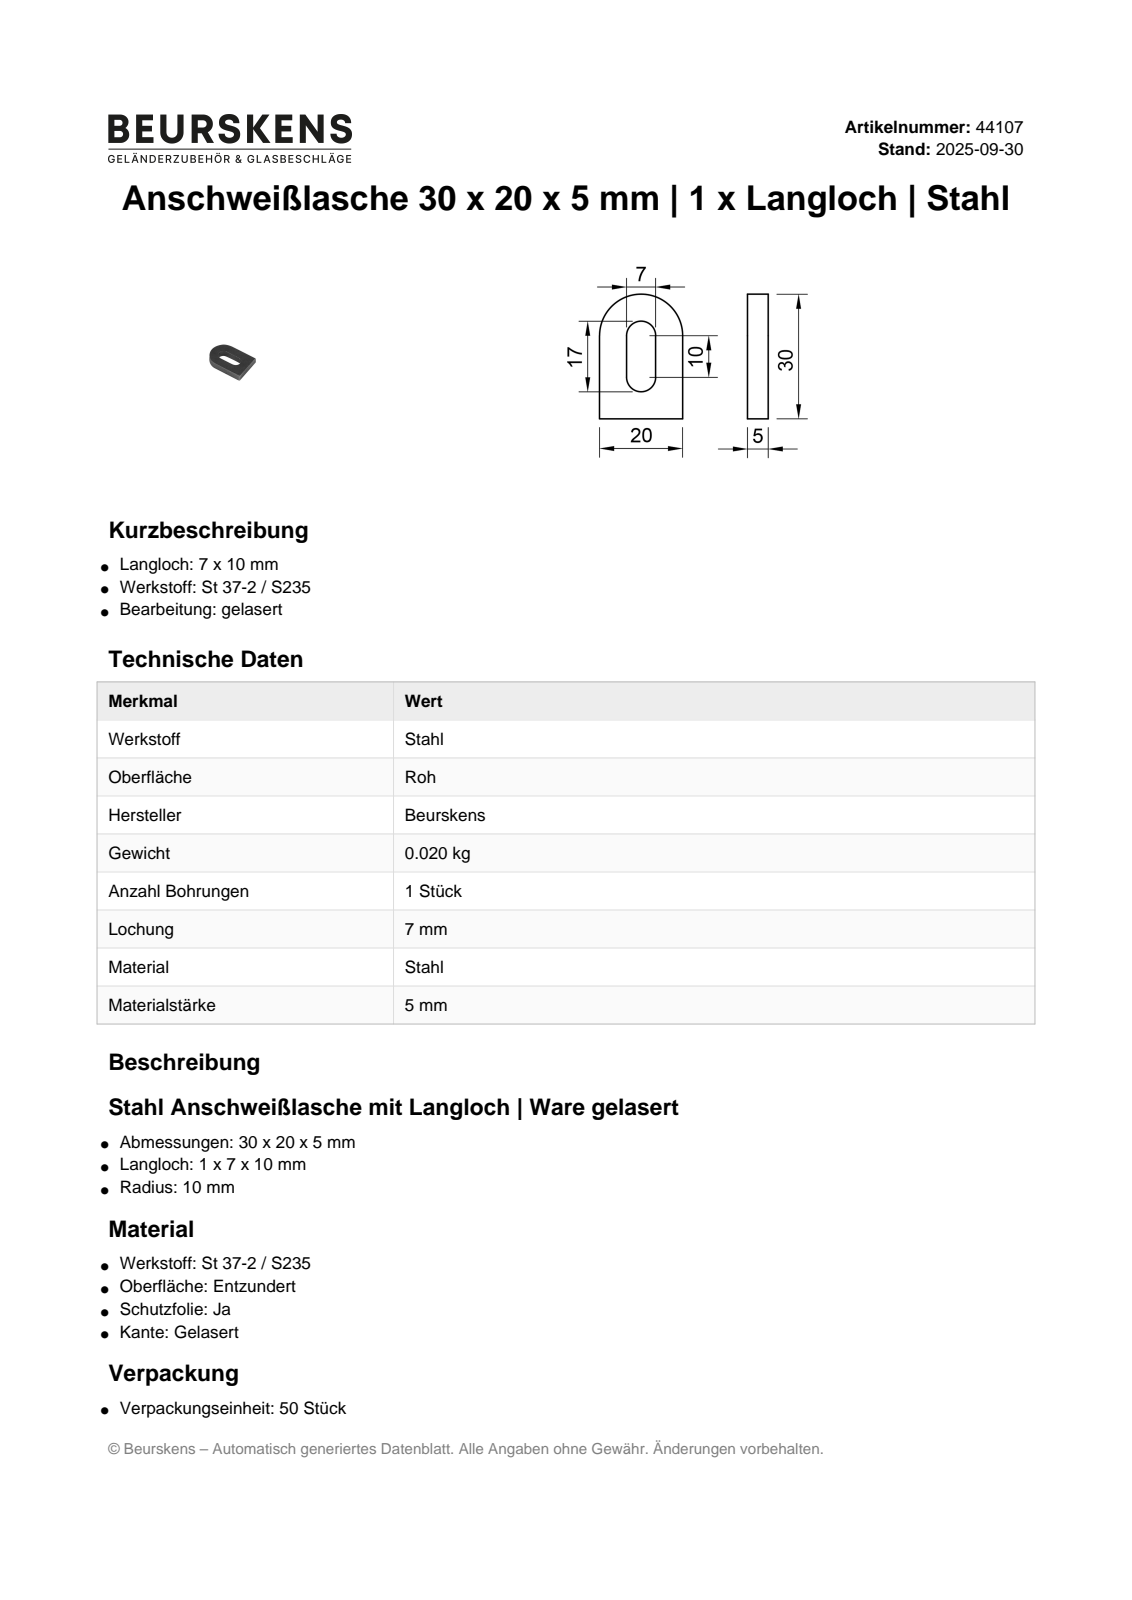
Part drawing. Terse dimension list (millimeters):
name: 44107
written by: Autodesk Inventor 2023 (AUTOMOTIVE_DESIGN)
unit: mm
bodies: 1 solid, 10 faces (7 planar, 3 cylindrical, 0 other)
size: 30 × 20 × 5
volume: 2 243 mm³; area: 1 564 mm²
rounds: 2× R3.5, 1× R10
face distances: 5, 6.5, 13.5, 20, 7
